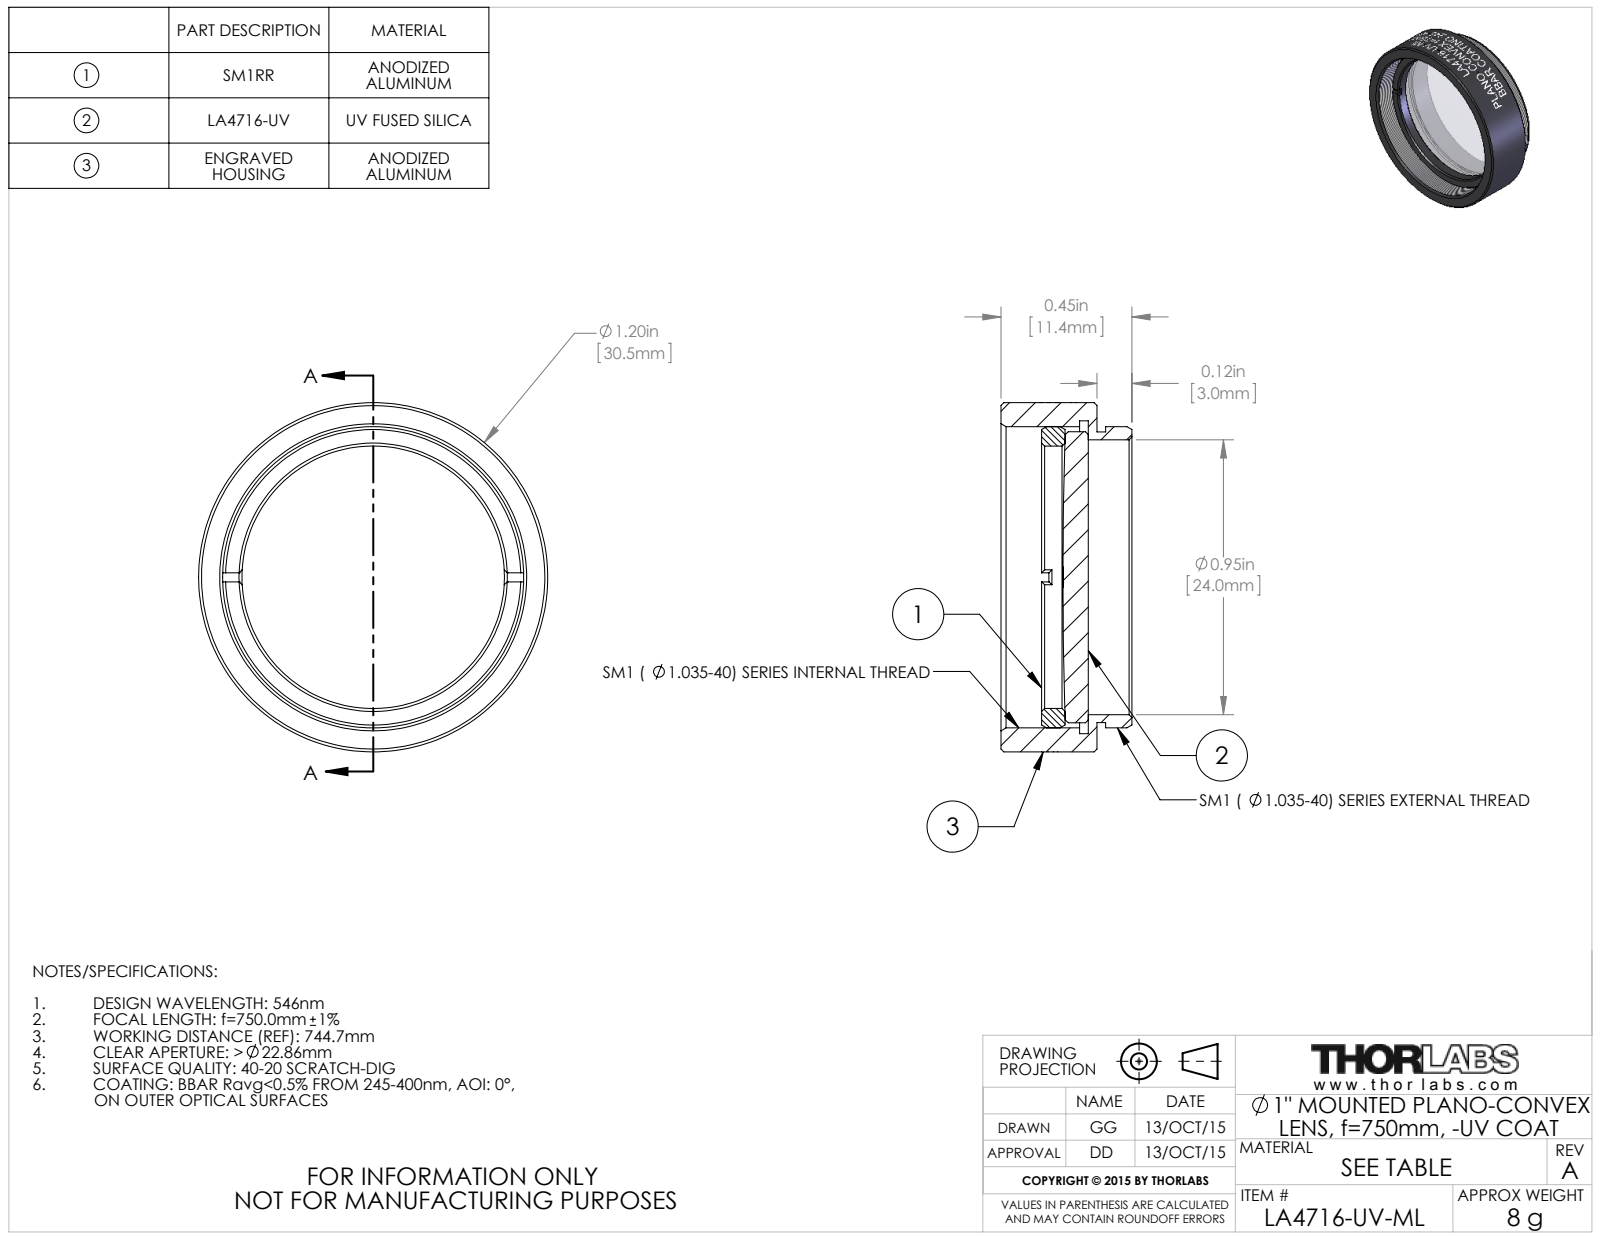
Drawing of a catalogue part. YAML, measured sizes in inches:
part_name: "TTN039357-E0W"
step_written_by: "SolidWorks 2014 (CONFIG_CONTROL_DESIGN)"
units: inches
bodies: {solids: 3, faces: 160, planar: 20, cylindrical: 112, other: 28}
overall_size: [1.2, 1.2, 0.45]
volume: 0.192
surface_area: 6.65
round_holes:
  - {diameter: 0.902, count: 1}
  - {diameter: 0.945, count: 1}
  - {diameter: 1.075, count: 1}
round_bosses_or_shafts:
  - {diameter: 1.2, count: 1}
  - {diameter: 1.035, count: 1}
  - {diameter: 1, count: 1}
  - {diameter: 0.999, count: 1}
face_to_face_distances: [0.03, 0.33, 0.3, 0.11, 0.08, 0.22, 0.19, 0.16, 0.08, 0.14]
